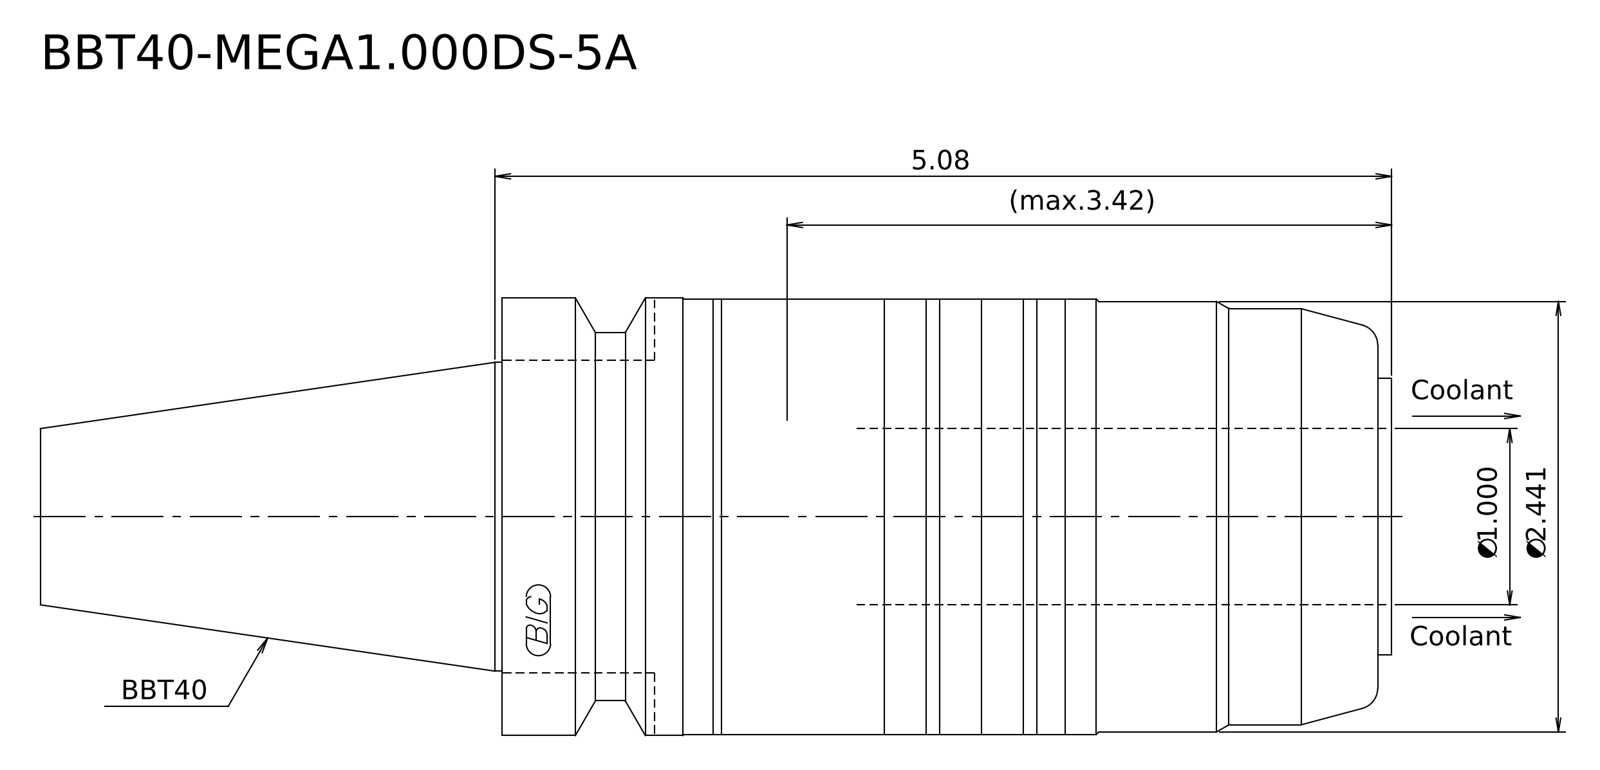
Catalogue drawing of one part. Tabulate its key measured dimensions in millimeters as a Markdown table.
| quantity | value |
| --- | --- |
| STEP written by | Kubotek KeyCreator 2011 V10.0.2 (22737) (automotive_design) |
| units | millimeters |
| bodies | 1 solid, 20 faces (4 planar, 8 cylindrical, 8 other) |
| overall size | 194.4 × 63 × 63 |
| volume | 441 202 mm³ |
| surface area | 37 493 mm² |
| round bosses / shafts (diameter × count) | 63 × 1, 62.7 × 1, 62 × 1, 59.9 × 1, 53 × 1, 44.45 × 1, 39.84 × 1 |
| main face-to-face distances | 128, 2, 126, 194.4, 192.4, 66.4 |
